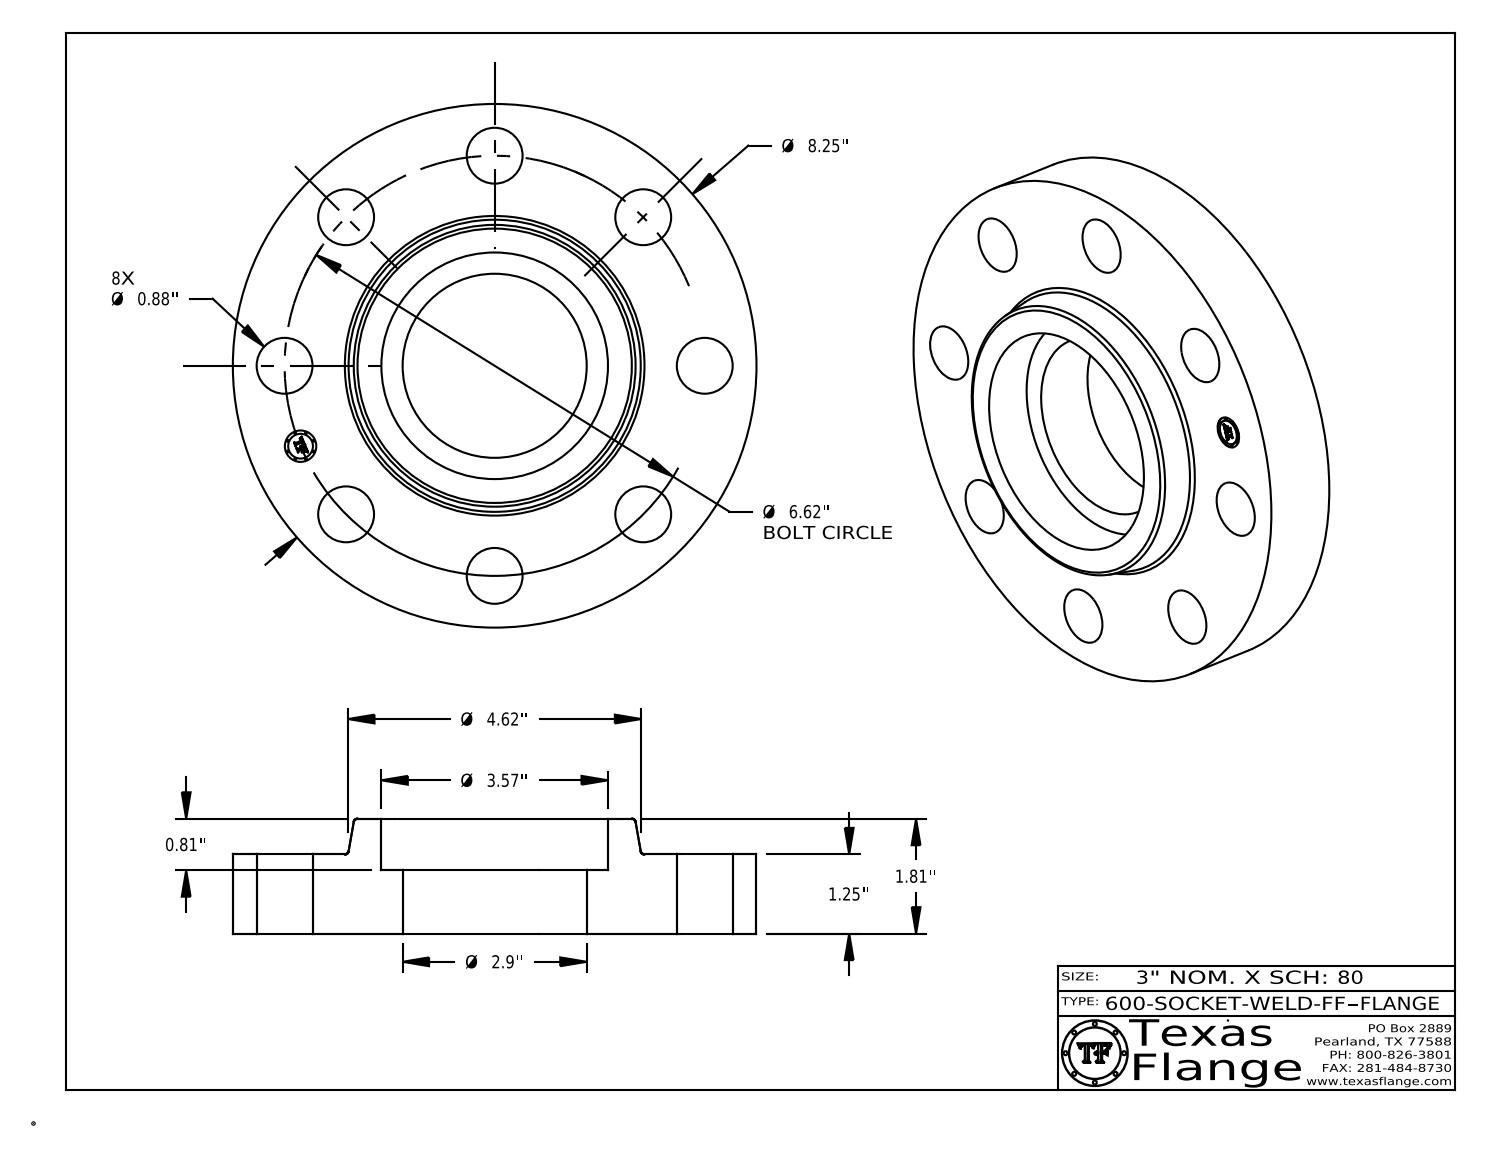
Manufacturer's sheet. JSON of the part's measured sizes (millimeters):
{"part_name": "600-SOCKET-WELD-FF", "step_written_by": "CATIA V5 STEP AP214 (AUTOMOTIVE_DESIGN)", "units": "millimeters", "bodies": {"solids": 1, "faces": 417, "planar": 369, "cylindrical": 42, "other": 6}, "overall_size": [209.6, 209.6, 46], "volume_mm3": 901600, "surface_area_mm2": 108700, "round_holes": [[22.4, 8], [12.6, 1], [73.7, 1], [90.7, 1]], "round_bosses_or_shafts": [[0.8, 8], [209.6, 1], [9.9, 1]], "face_to_face_distances": [31.8, 46, 14.2, 25.4, 6.4, 20.6, 0.4, 31.4, 6, 14.6], "hole_center_spacings": [84.1, 64.3, 155.3, 118.9, 118.9, 32.8, 93.4, 164.9]}
